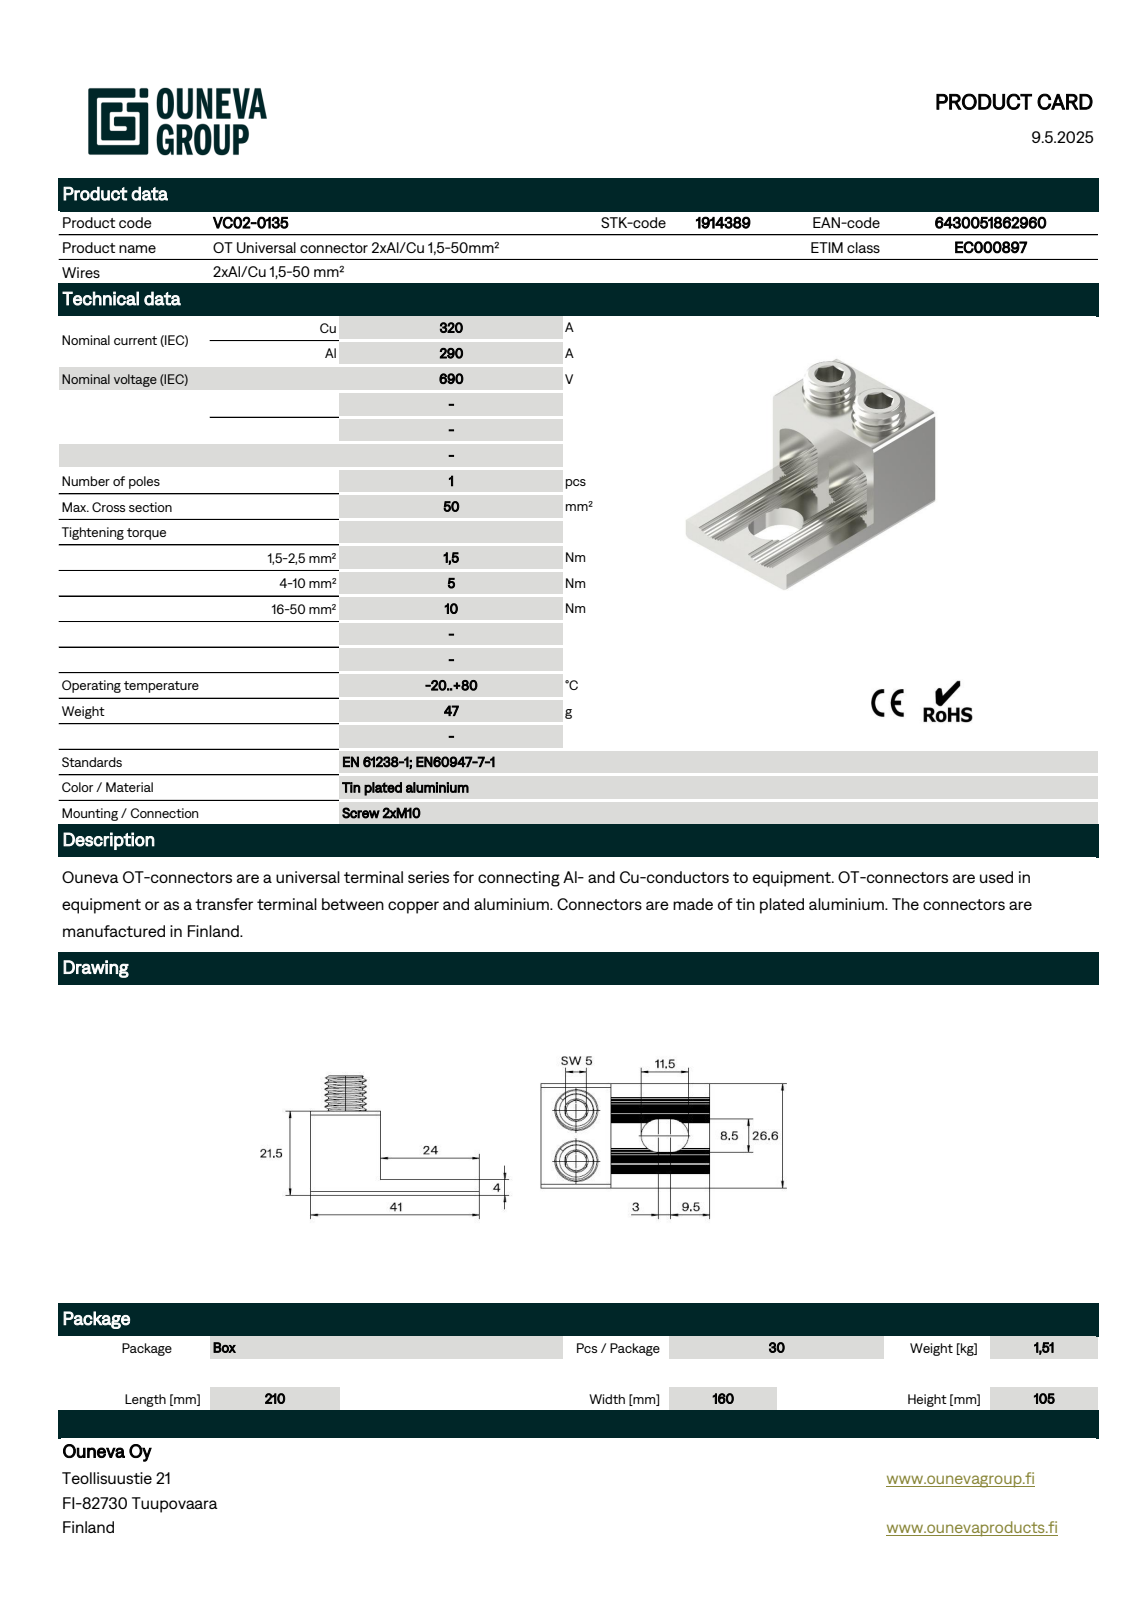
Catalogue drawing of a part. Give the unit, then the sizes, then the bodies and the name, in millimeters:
Units: millimetres
Overall size (bounding box): 41 × 26.6 × 25
Round bosses / shafts (diameter × count): ⌀9.8 ×2
Partial cylindrical surfaces — rounded edges, fillets, slot ends (radius × count): R0.1 ×58, R1 ×8, R0.25 ×4, R4.25 ×2, R7.76 ×2
Main face-to-face distances: 26.6, 21.5, 11.8, 14.8, 1.8, 24.8, 10, 13, 4, 17.5
Volume: 9 045 mm³ · Surface area: 5 835 mm²
Bodies: 1 solid, 199 faces (101 planar, 90 cylindrical, 8 other)
Part name (STEP PRODUCT): Liitinrunko OT 2x50
STEP written by: Creo Elements/Direct Modeling 20.6A 14-Oct-2023 (C) Parametric Technology GmbH (AUTOMOTIVE_DESIGN)
